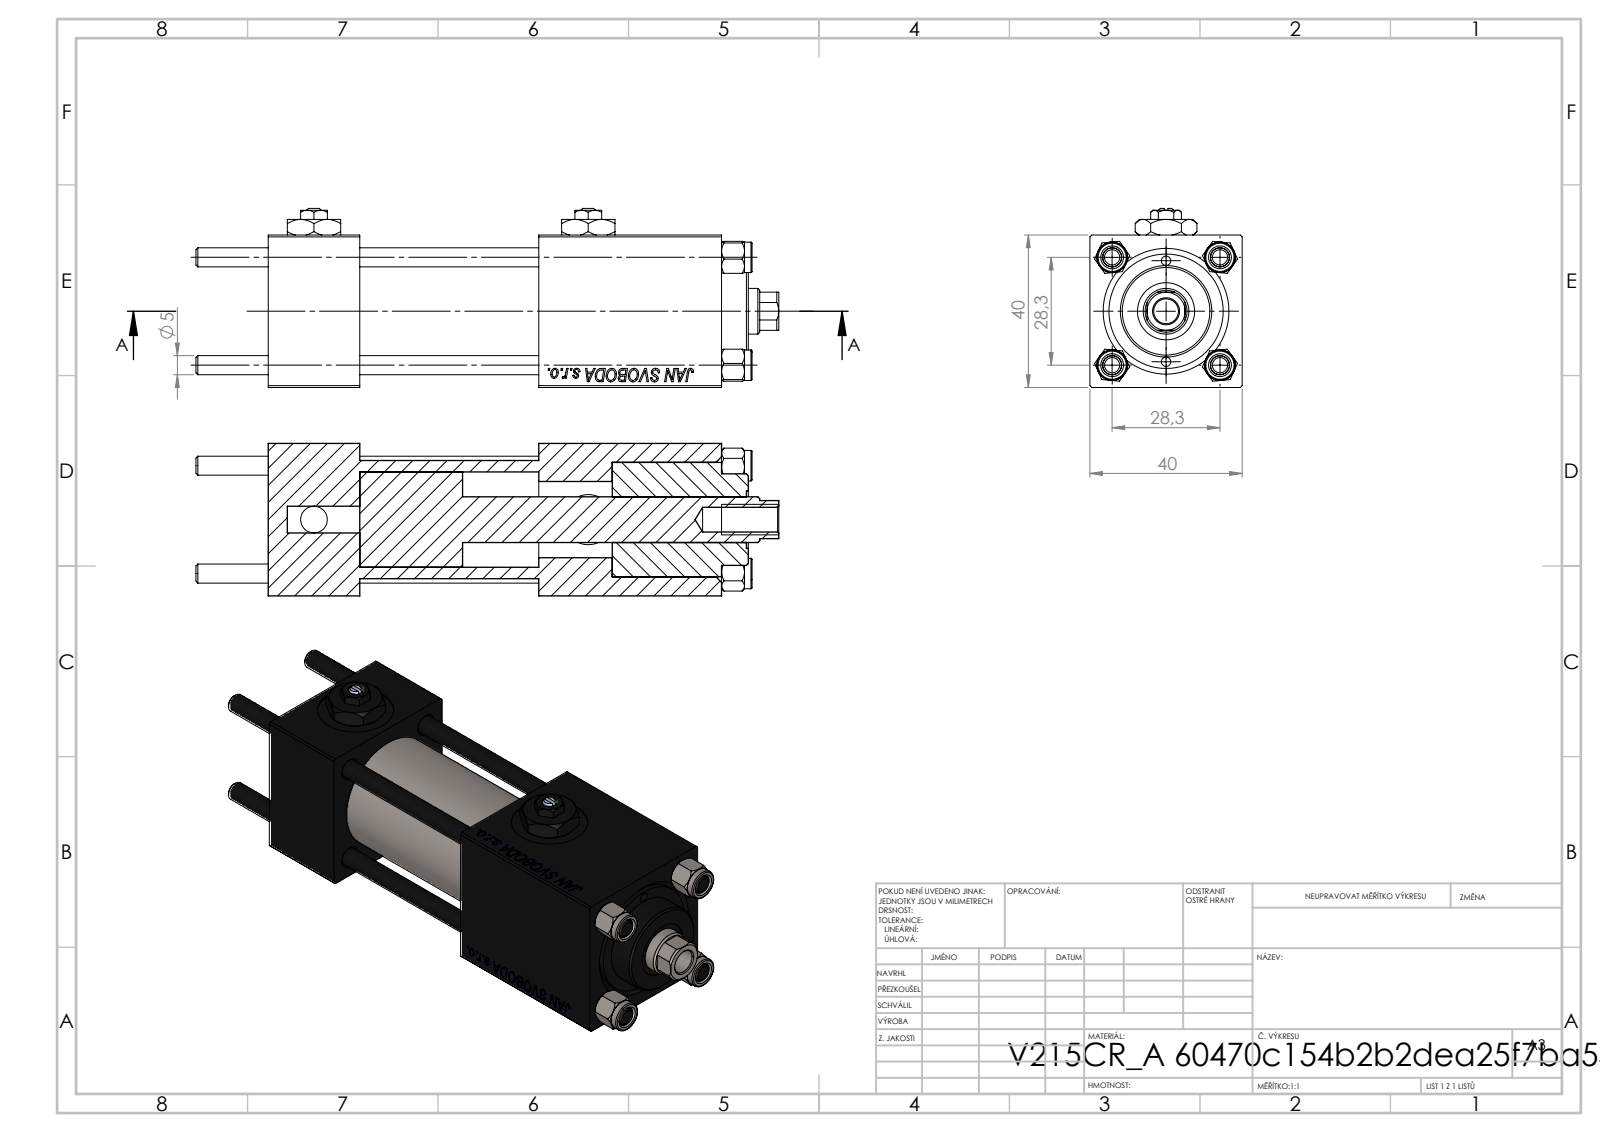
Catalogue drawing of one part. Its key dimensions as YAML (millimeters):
part_name: "CR025_012_A_0_G_A_G_M_020_+#_##_TYCINKA; Zatka_pro_OIL_PORT; NUT_M5; V215CR_VCP (+2 more)"
step_written_by: "SolidWorks 2019 (CONFIG_CONTROL_DESIGN)"
units: millimeters
bodies: {solids: 13, faces: 1238, planar: 566, cylindrical: 94, other: 578}
overall_size: [153, 47, 40]
volume: 143371
surface_area: 60718
round_holes:
  - {diameter: 5, count: 4}
  - {diameter: 20, count: 3}
  - {diameter: 2.5, count: 2}
  - {diameter: 7, count: 2}
  - {diameter: 13.16, count: 2}
  - {diameter: 6.5, count: 1}
  - {diameter: 12, count: 1}
  - {diameter: 15, count: 1}
  - {diameter: 25, count: 1}
  - {diameter: 30, count: 1}
round_bosses_or_shafts:
  - {diameter: 8, count: 4}
  - {diameter: 31, count: 1}
  - {diameter: 24, count: 1}
partial_cylinders:
  - {radius: 5.5, count: 1}
face_to_face_distances: [40, 24, 39.8, 95, 119, 90.3, 66.3, 28.7, 47, 71]
hole_center_spacings: [14.18, 20.01, 28.3, 30.84, 13.25, 40.02, 26.5, 72]
